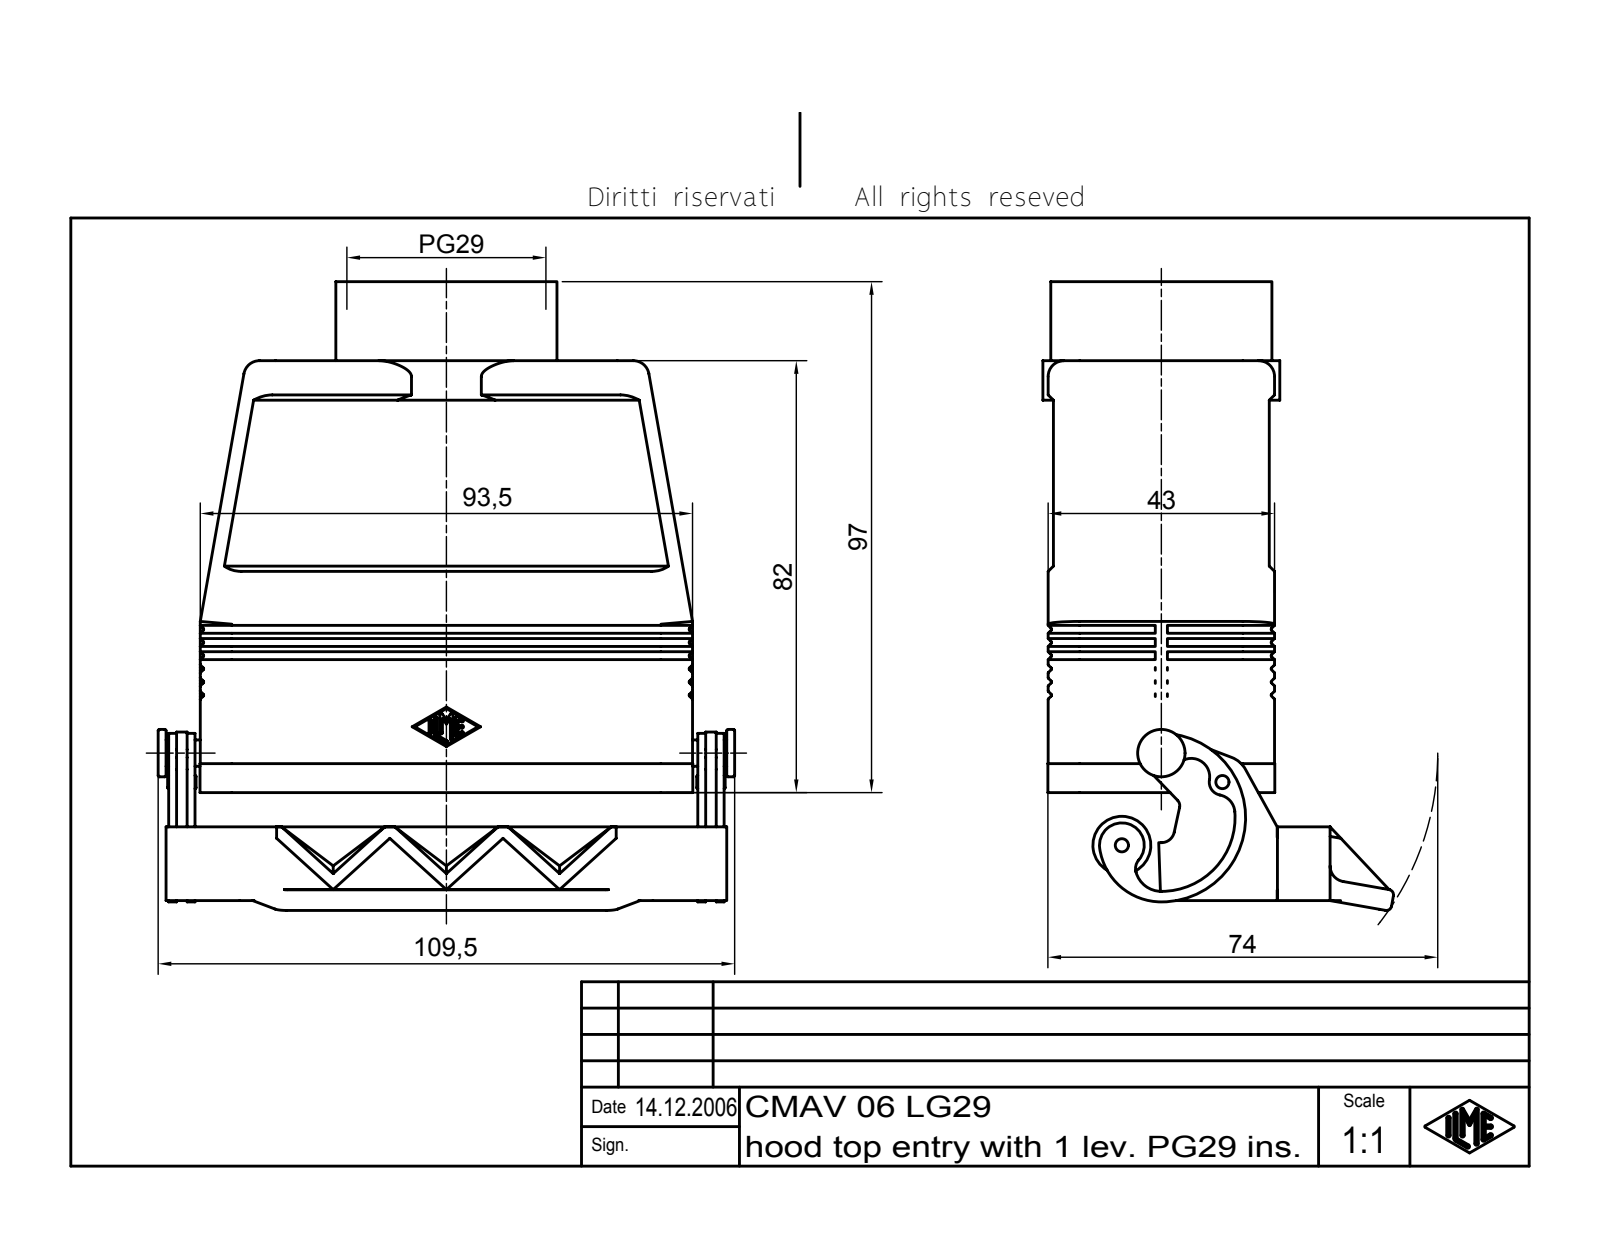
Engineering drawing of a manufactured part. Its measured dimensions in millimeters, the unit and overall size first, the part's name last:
Units: millimetres
Overall size (bounding box): 119.37 × 109.5 × 66.59
Round holes (diameter × count): ⌀2.5 ×1, ⌀33.48 ×1, ⌀35.48 ×1
Round bosses / shafts (diameter × count): ⌀45 ×1, ⌀42 ×1, ⌀11 ×1, ⌀9 ×1, ⌀5 ×1, ⌀3.1 ×1, ⌀2 ×1
Partial cylindrical surfaces — rounded edges, fillets, slot ends (radius × count): R0.2 ×52, R0.25 ×32, R2.5 ×9, R6 ×8, R3 ×7, R1 ×6, R2.45 ×4, R6.05 ×4
Main face-to-face distances: 3.45, 3.5, 39.55, 39.5, 36.05, 36.1, 36, 2.45, 1, 38.55
Volume: 104 816 mm³ · Surface area: 61 733 mm²
Bodies: 1 solid, 947 faces (222 planar, 324 cylindrical, 401 other)
Part name (STEP PRODUCT): CMAV 06 LG29
STEP written by: Autodesk Inventor 7 (AUTOMOTIVE_DESIGN)
